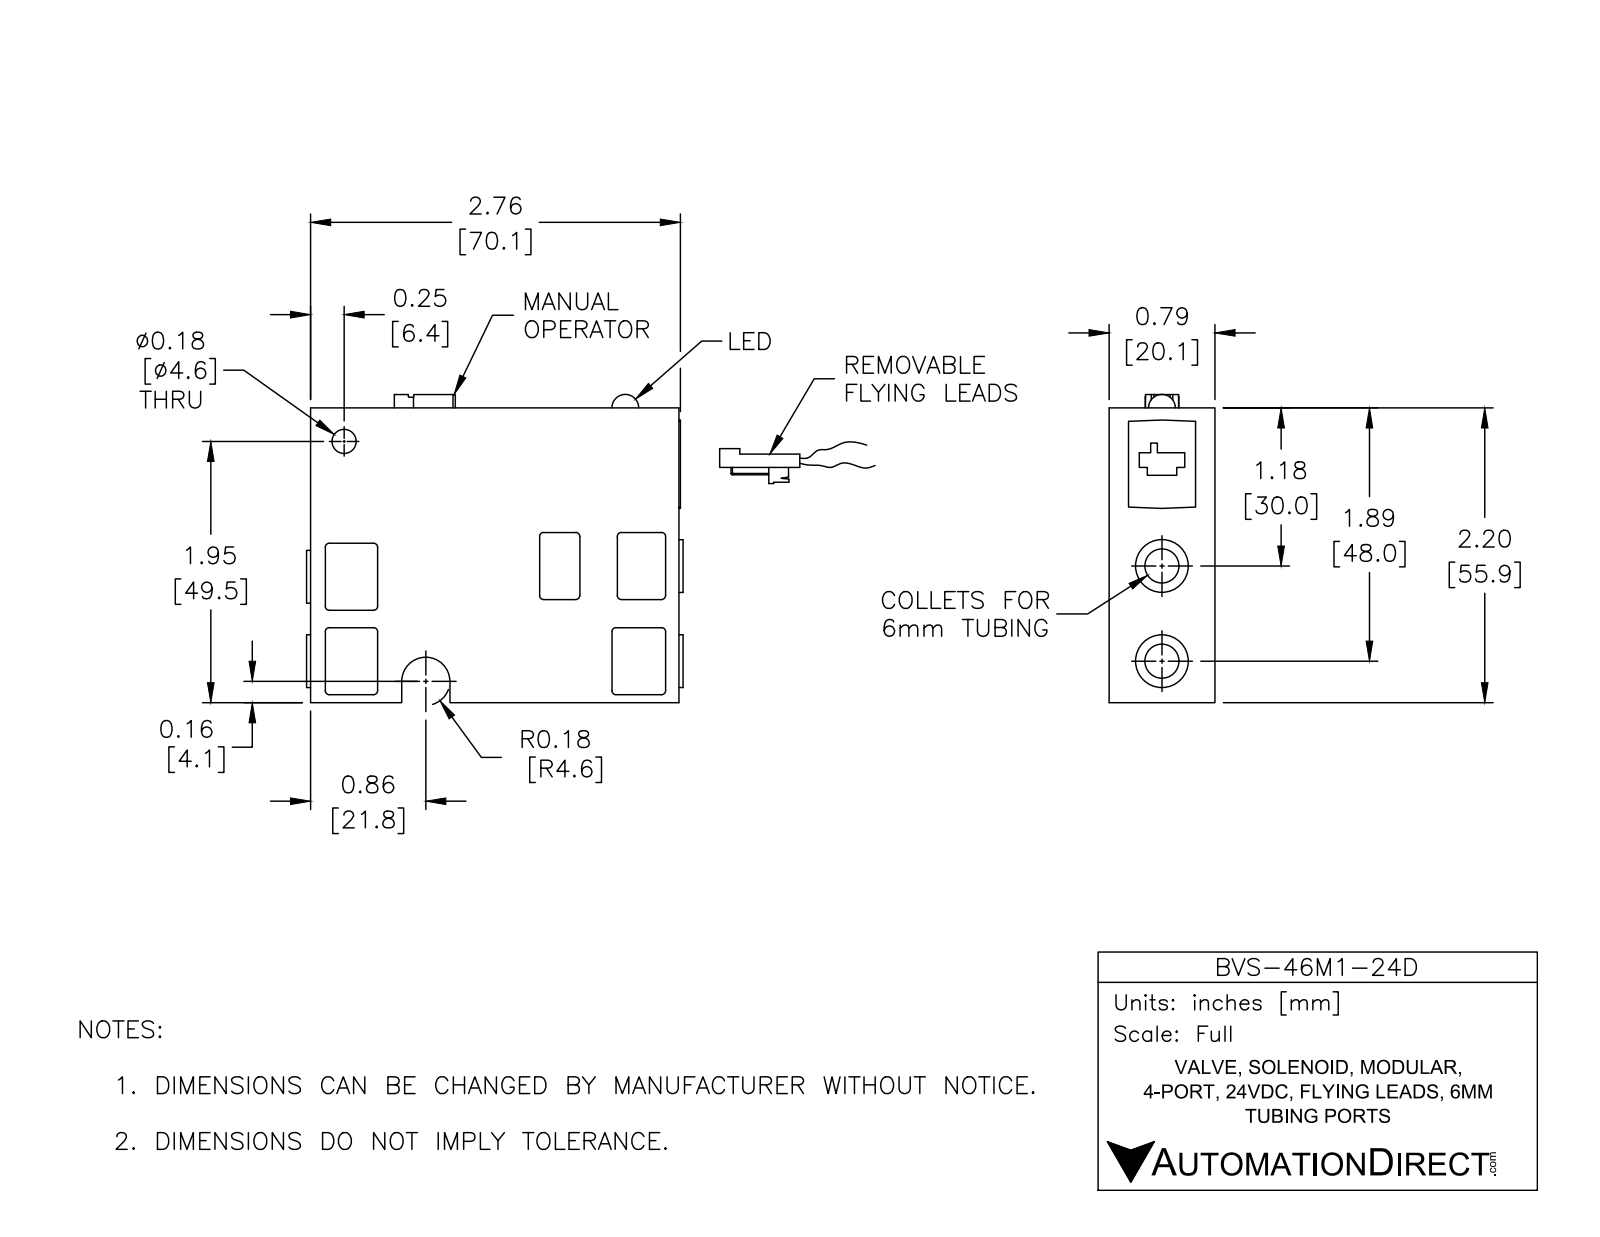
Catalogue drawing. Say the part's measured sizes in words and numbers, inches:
The part is named "BVS-46M1-24D". Its 3-D file was written by "SolidWorks 2016 (AUTOMOTIVE_DESIGN)". It is 1 solid with 173 faces: 85 planar, 78 cylindrical and 10 other. Overall it measures 3.009 by 2.3 by 0.79 inches. Its volume is 4.377 cubic inches and its surface area 25.04 square inches. Round holes: 3 of diameter 0.25, 1 of diameter 0.1, 1 of diameter 0.18. Round bosses or shafts: 6 of diameter 0.06, 3 of diameter 0.394. Partial cylindrical surfaces (rounded edges, fillets, slot ends): 20 of radius 0.03, 2 of radius 0.02, 1 of radius 0.125, 1 of radius 0.18. The main face-to-face distances are 0.79, 0.1, 2.2, 0.69, 2.75, 0.59, 0.5, 0.11, 2.65, 2.76. The hole center spacings are 0.08, 0.55, 0.63, 0.63, 0.71, 1.26.
